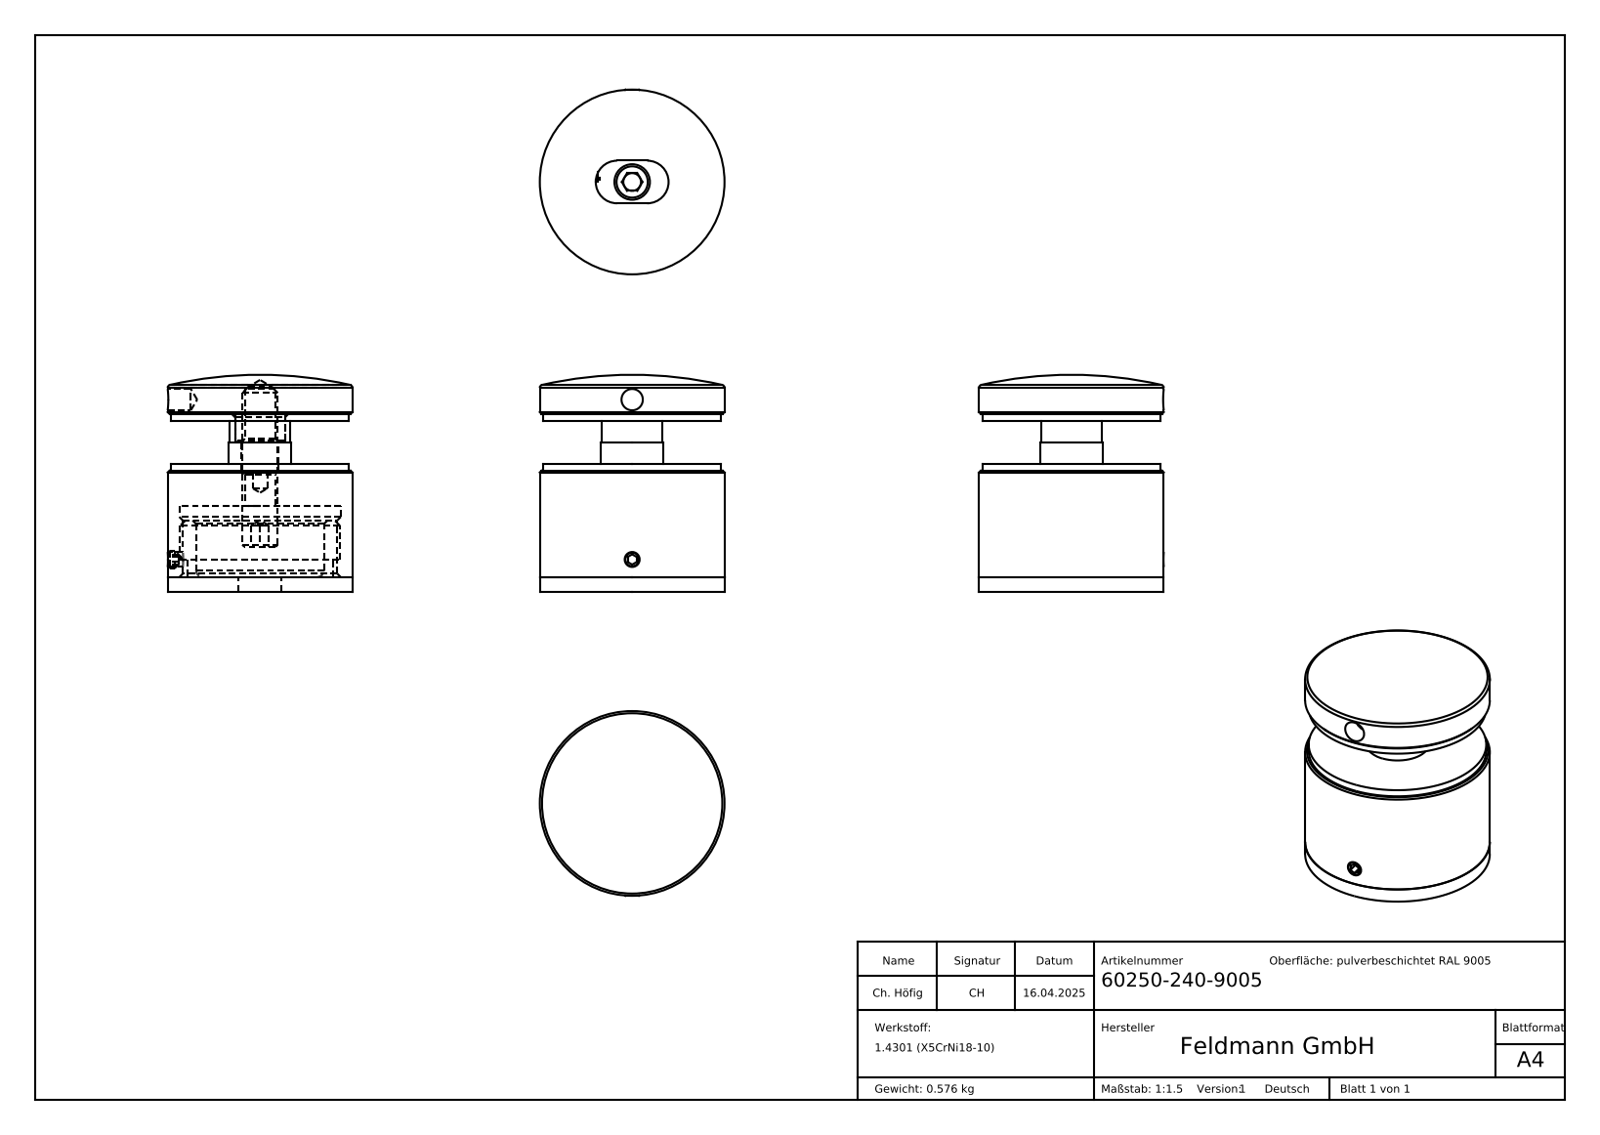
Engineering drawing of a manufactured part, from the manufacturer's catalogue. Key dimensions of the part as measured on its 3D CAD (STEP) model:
Part name (STEP PRODUCT): 60250-XXX Teil3_60250-240-9005 Teil3; 60250-XXX Teil5_60250-XXX Teil5; 60250-XXX Teil4_60250-XXX Teil4; 60250-XXX Teil6_60250-XXX Teil6 (+5 more)
STEP written by: SolidWorks 2018 (CONFIG_CONTROL_DESIGN)
Units: millimetres
Bodies: 8 solids, 427 faces (213 planar, 26 cylindrical, 188 other)
Overall size (bounding box): 61 × 52 × 52
Volume: 80 319 mm³ · Surface area: 38 873 mm²
Round holes (diameter × count): ⌀4 ×2, ⌀4.2 ×1, ⌀6 ×1, ⌀8.5 ×1, ⌀10.5 ×1, ⌀14 ×1, ⌀36 ×1, ⌀43.5 ×1, ⌀45.5 ×1
Round bosses / shafts (diameter × count): ⌀52 ×1, ⌀50 ×1, ⌀45 ×1, ⌀41 ×1, ⌀17.5 ×1, ⌀17 ×1, ⌀10 ×1, ⌀5 ×1
Partial cylindrical surfaces — rounded edges, fillets, slot ends (radius × count): R6 ×2
Main face-to-face distances: 16, 14, 2, 12, 24, 4, 30, 34, 36, 50
Hole centre spacings: 16.5, 33, 45
